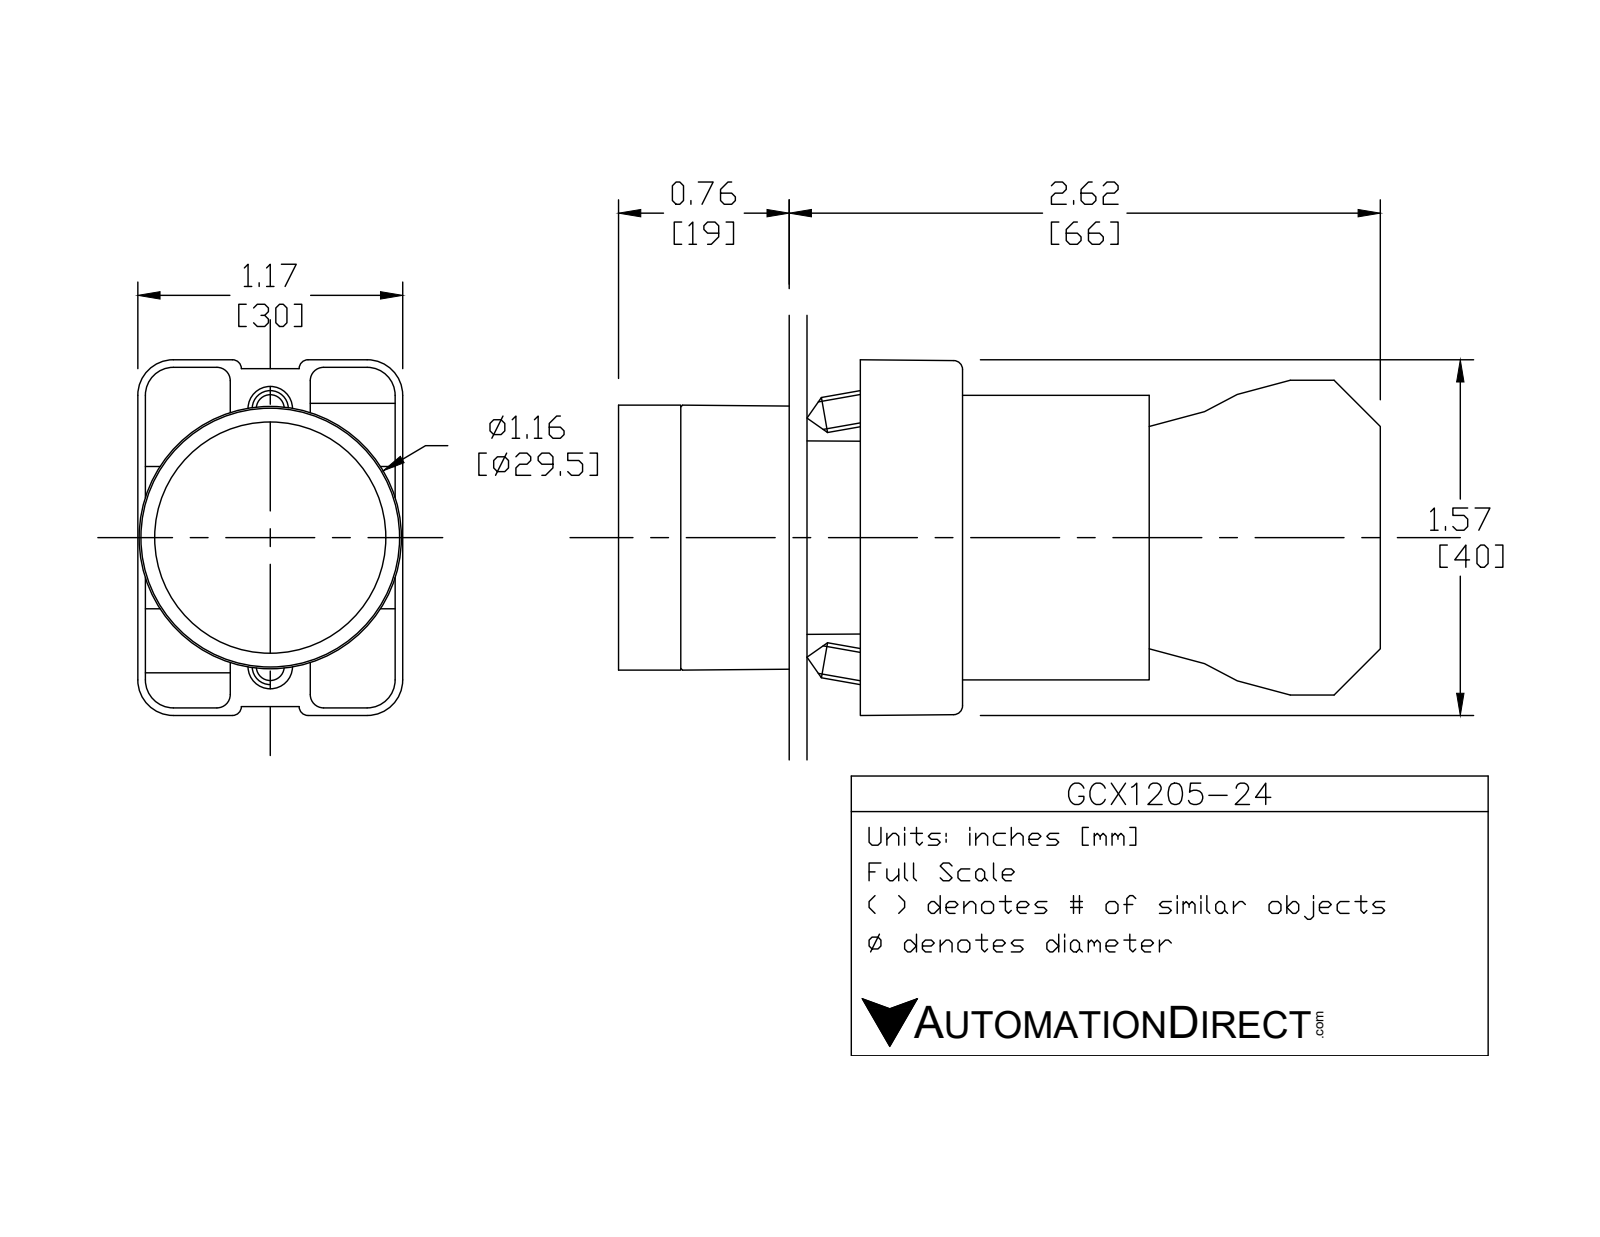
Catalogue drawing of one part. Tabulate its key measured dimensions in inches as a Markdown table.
| quantity | value |
| --- | --- |
| part name | ECX1050; GCX1205 OPERATOR; ecx1040; ecx1029 (+1 more) |
| STEP written by | SolidWorks 2016 (AUTOMOTIVE_DESIGN) |
| units | inches |
| bodies | 8 solids, 431 faces (252 planar, 148 cylindrical, 31 other) |
| overall size | 3.319 × 1.581 × 1.177 |
| volume | 2.794 in³ |
| surface area | 38.75 in² |
| round holes (diameter × count) | 0.079 × 2, 0.124 × 2, 0.13 × 2, 0.087 × 1, 0.197 × 1, 0.469 × 1, 0.878 × 1, 0.888 × 1, 1.024 × 1 |
| round bosses / shafts (diameter × count) | 0.157 × 4, 1.175 × 1, 1.004 × 1, 0.945 × 1, 0.856 × 1, 0.78 × 1, 0.504 × 1 |
| partial cylindrical surfaces (radius × count) | 0.059 × 24, 0.041 × 12, 0.124 × 12, 0.157 × 12, 0.039 × 8, 0.128 × 2, 0.02 × 1, 0.063 × 1 |
| main face-to-face distances | 0.827, 2.02, 1.193, 0.579, 1.171, 0.031, 0.276, 0.033, 0.748, 0.573 |
| hole center spacings | 0.236, 0.544, 0.472, 0.49 |
